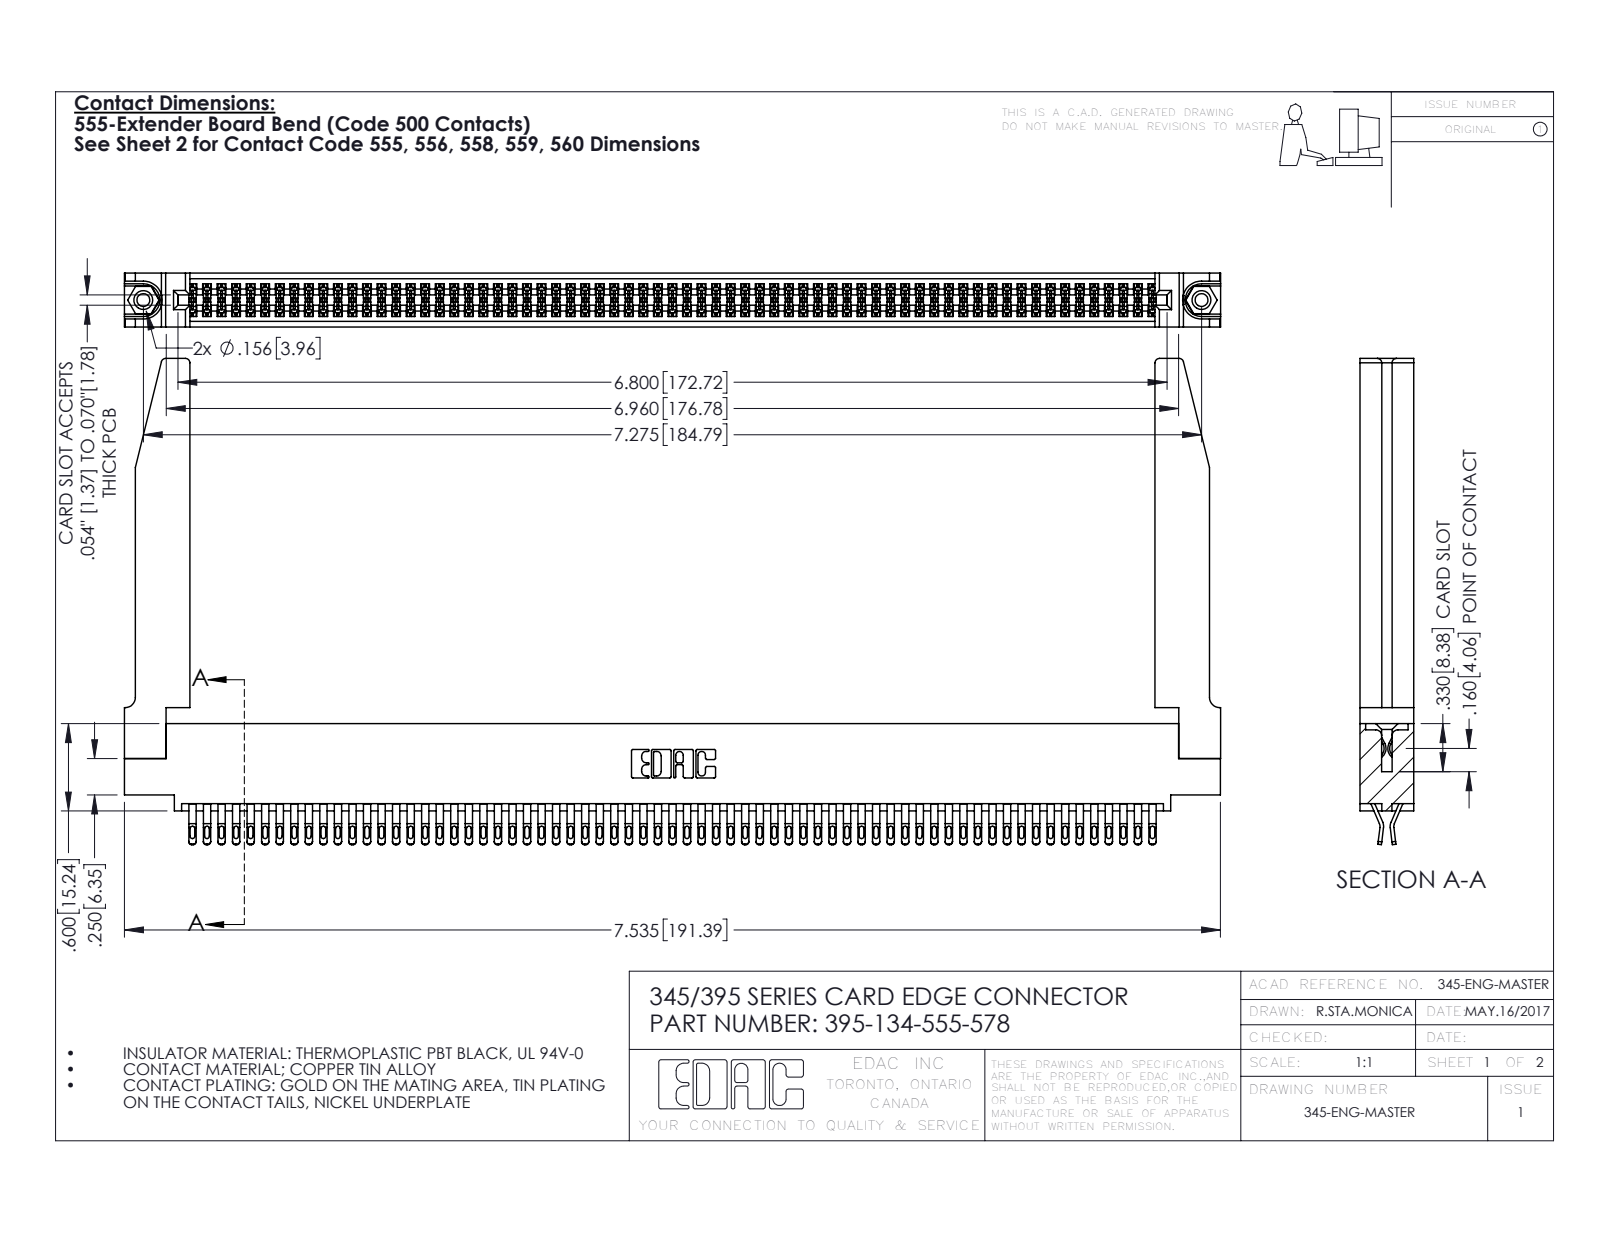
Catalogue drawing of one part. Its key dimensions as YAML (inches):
part_name: "395-134-555-578; 345 Part_0.110 Offset - 0.156 Dia-TH; 345-220-078_345-220-078; 345-250-001_345-250-001-102 (+1 more)"
step_written_by: "SolidWorks 2016 (CONFIG_CONTROL_DESIGN)"
units: inches
bodies: {solids: 139, faces: 7868, planar: 4380, cylindrical: 3436, other: 52}
overall_size: [7.536, 3.342, 0.37]
volume: 1.642
surface_area: 57.45
round_holes:
  - {diameter: 0.089, count: 2}
  - {diameter: 0.125, count: 2}
  - {diameter: 0.156, count: 2}
  - {diameter: 0.064, count: 1}
round_bosses_or_shafts:
  - {diameter: 0.155, count: 2}
partial_cylinders:
  - {radius: 0.016, count: 335}
  - {radius: 0.02, count: 268}
  - {radius: 0.006, count: 201}
  - {radius: 0.01, count: 22}
  - {radius: 0.03, count: 8}
  - {radius: 0.007, count: 6}
  - {radius: 0.031, count: 6}
  - {radius: 0.026, count: 3}
face_to_face_distances: [0.072, 0.298, 0.37, 0.025, 0.098, 0.272, 0.2, 0.225, 0.175, 0.149]
hole_center_spacings: [0.27, 7.039, 7.275]
